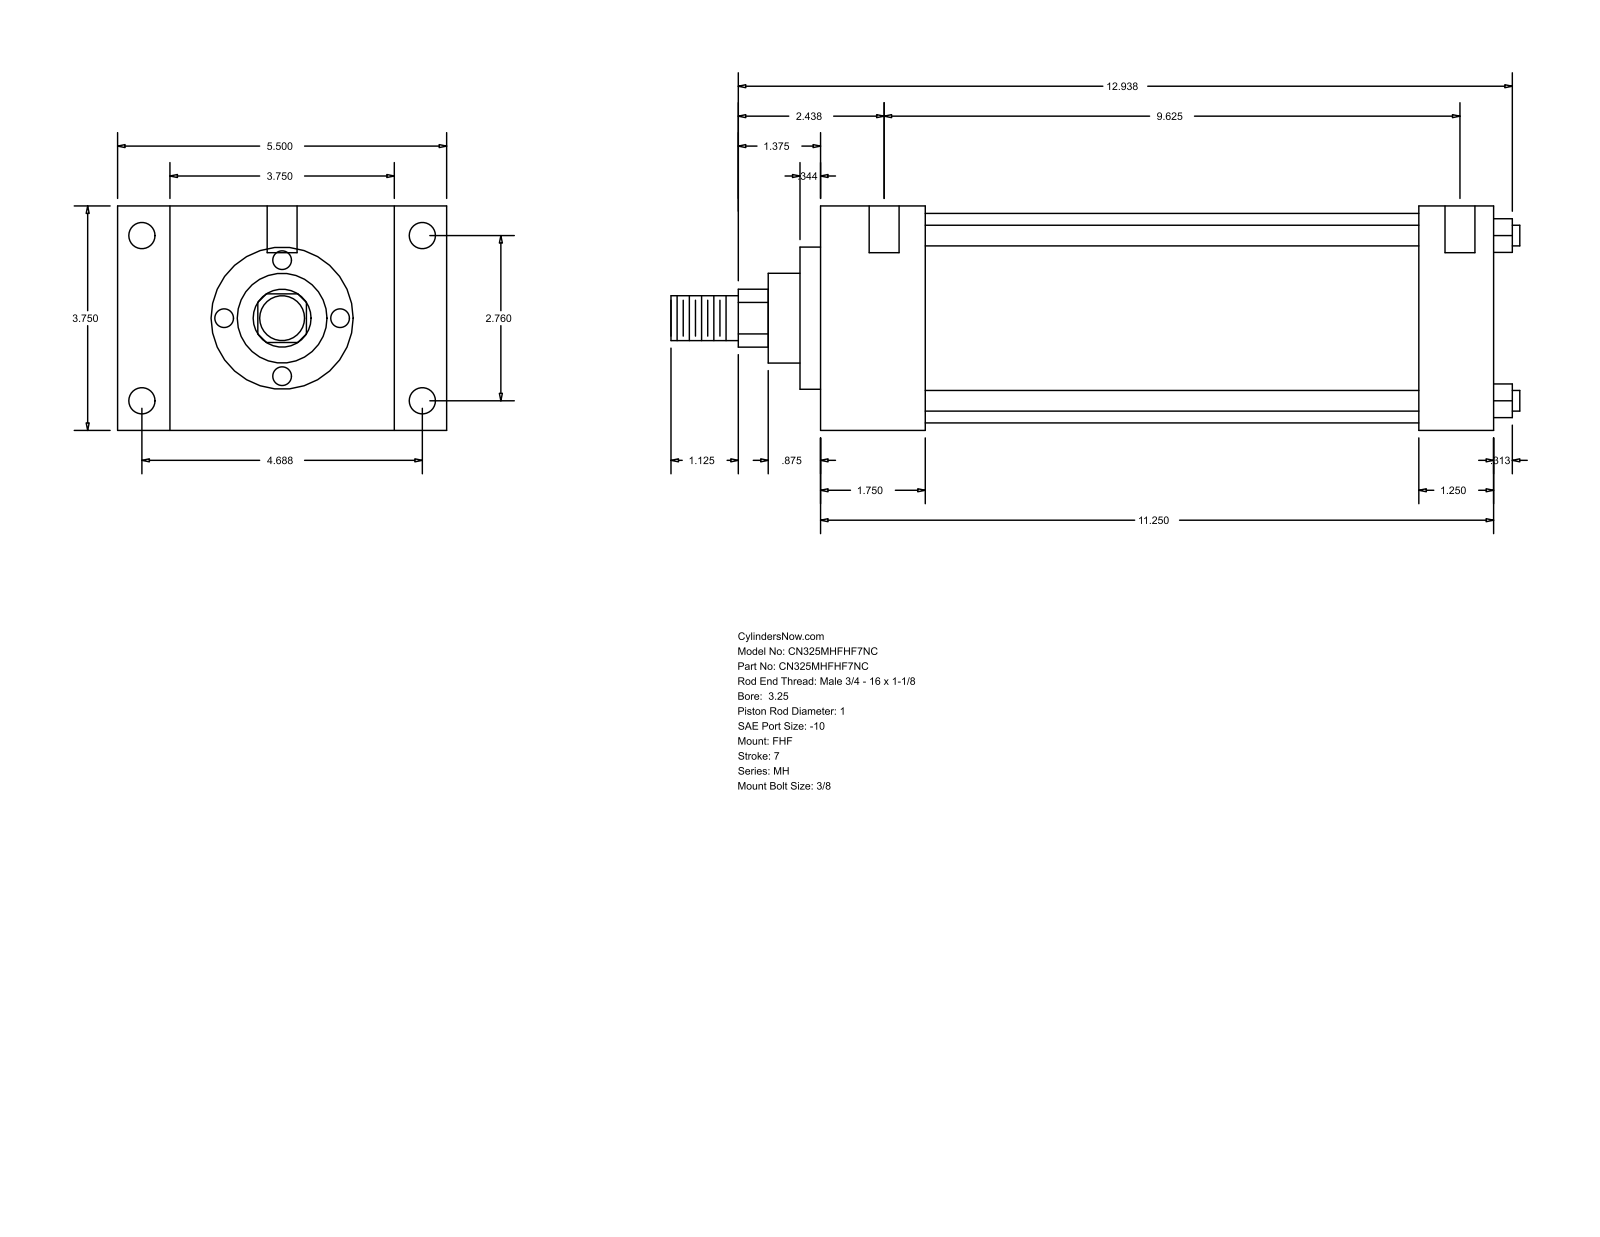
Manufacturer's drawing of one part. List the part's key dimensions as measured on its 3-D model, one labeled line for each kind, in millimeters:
Part name (STEP PRODUCT): MH_FHF__0325_1
STEP written by: GSSL Pune (CONFIG_CONTROL_DESIGN)
Units: millimetres
Bodies: 0 solids, 90 faces (61 planar, 29 cylindrical, 0 other)
Overall size (bounding box): 360.36 × 139.7 × 95.25
Round holes (diameter × count): ⌀5.56 ×4, ⌀11.13 ×4, ⌀12.7 ×2
Round bosses / shafts (diameter × count): ⌀8.76 ×4, ⌀88.9 ×1, ⌀60.33 ×1, ⌀38.1 ×1, ⌀25.4 ×1, ⌀19.05 ×1
Partial cylindrical surfaces — rounded edges, fillets, slot ends (radius × count): R12.29 ×1
Main face-to-face distances: 95.24, 285.76, 44.46, 241.3, 22.23, 117.47, 139.7, 254.01, 209.55, 31.75
Hole centre spacings: 70.1, 119.06, 138.16, 250.82, 1.58, 4.76, 244.48, 246.06
